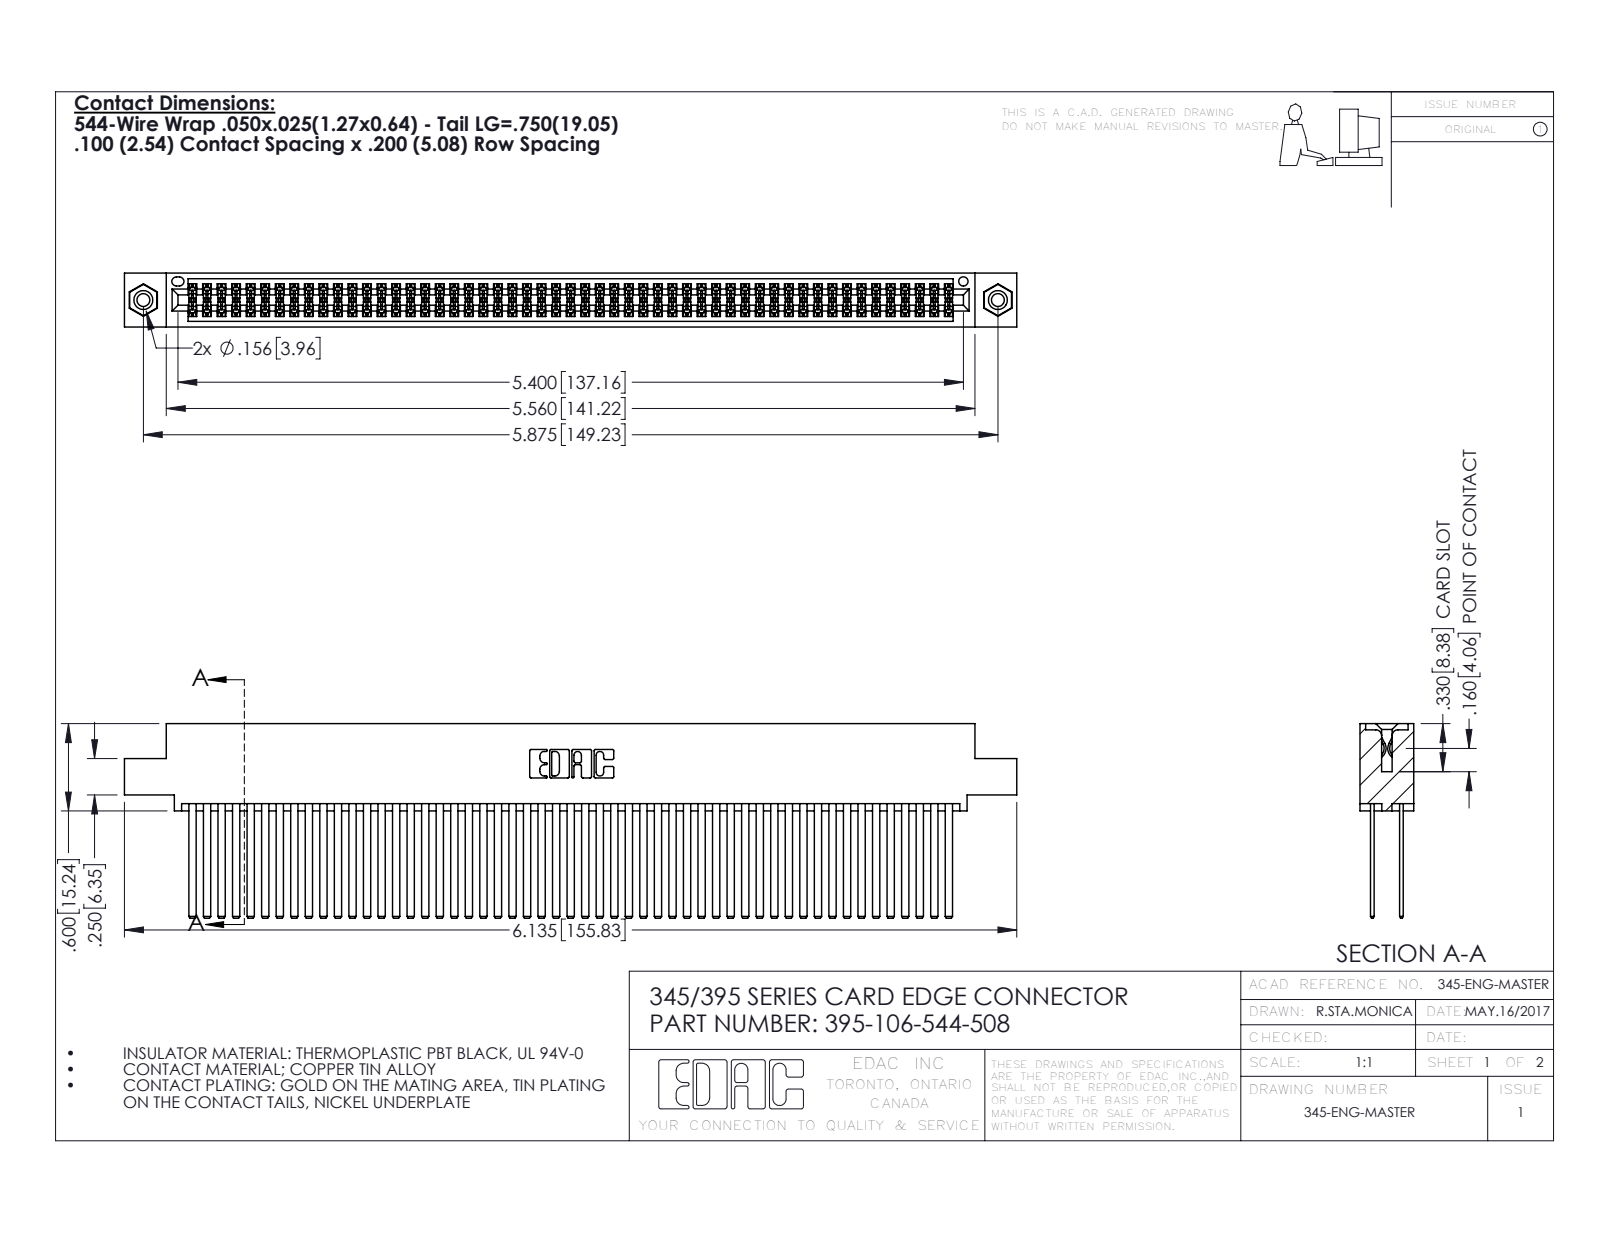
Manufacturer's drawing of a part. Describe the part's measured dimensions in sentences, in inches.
The part is named "345 Part_0.110 Offset - 0.156 Dia-TI; 345-250-001_345-250-003-102; 345-292-001_345-293-144; 395-106-544-508". Its 3-D file was written by "SolidWorks 2016 (CONFIG_CONTROL_DESIGN)". It is 109 solids with 4854 faces: 3190 planar, 1648 cylindrical and 16 other. Overall it measures 6.135 by 1.337 by 0.37 inches. Its volume is 1.016 cubic inches and its surface area 45.38 square inches. Round holes: 2 of diameter 0.089, 2 of diameter 0.125, 2 of diameter 0.156, 1 of diameter 0.064. Round bosses or shafts: 2 of diameter 0.155. Partial cylindrical surfaces (rounded edges, fillets, slot ends): 159 of radius 0.006, 22 of radius 0.01, 6 of radius 0.007, 6 of radius 0.031, 3 of radius 0.026, 2 of radius 0.014, 2 of radius 0.019, 2 of radius 0.022. The main face-to-face distances are 0.2, 0.025, 0.072, 0.098, 0.272, 0.298, 0.225, 0.175, 0.37, 0.05. The hole center spacings are 0.27, 5.639, 5.875.
